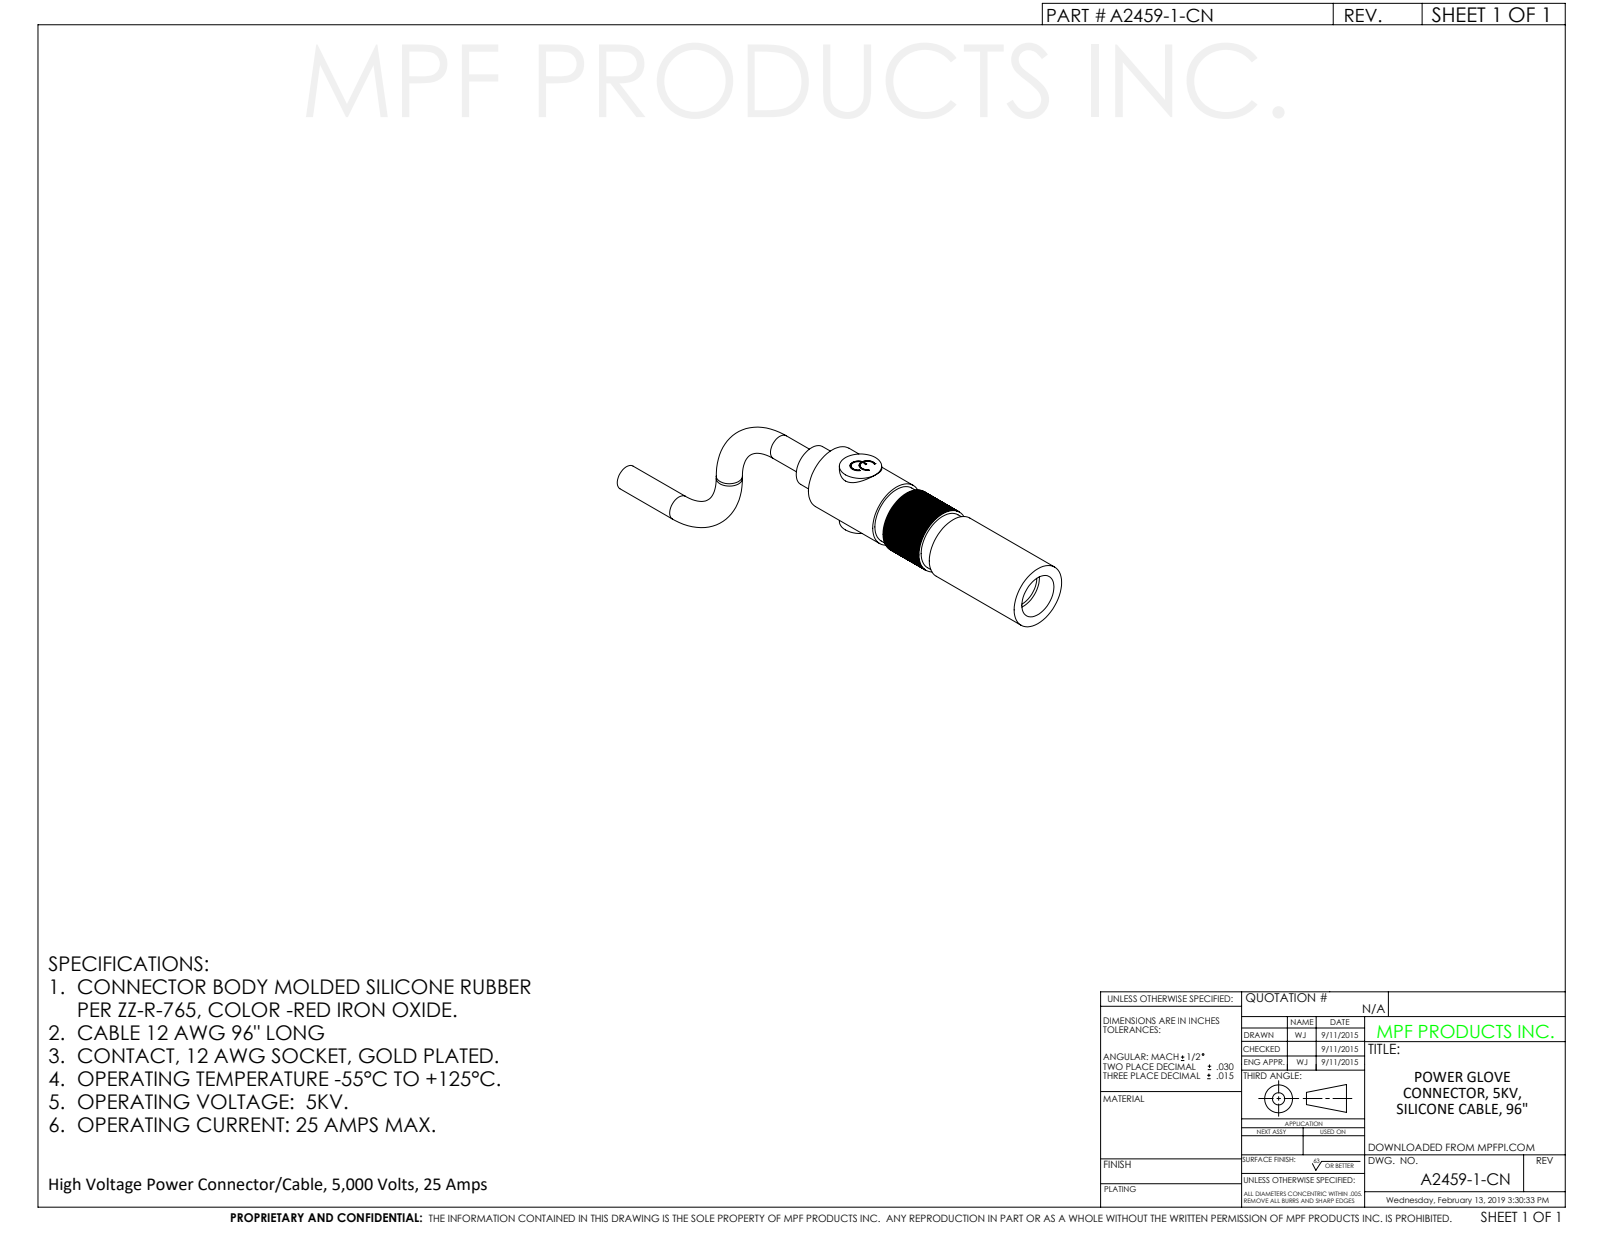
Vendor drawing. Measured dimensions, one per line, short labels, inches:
name: A2459-1-CN
written by: SolidWorks 2012 (CONFIG_CONTROL_DESIGN)
unit: in
bodies: 1 solid, 523 faces (15 planar, 18 cylindrical, 490 other)
size: 2.396 × 0.694 × 0.455
volume: 0.283 in³; area: 3.837 in²
holes: 1× ⌀0.28, 1× ⌀0.287, 1× ⌀0.313
bosses: 1× ⌀0.445, 1× ⌀0.427, 1× ⌀0.282, 1× ⌀0.219
face distances: 1.79, 1.43, 0.36, 0.481, 0.193, 1.623, 1.983, 1.893, 1.7, 0.27
